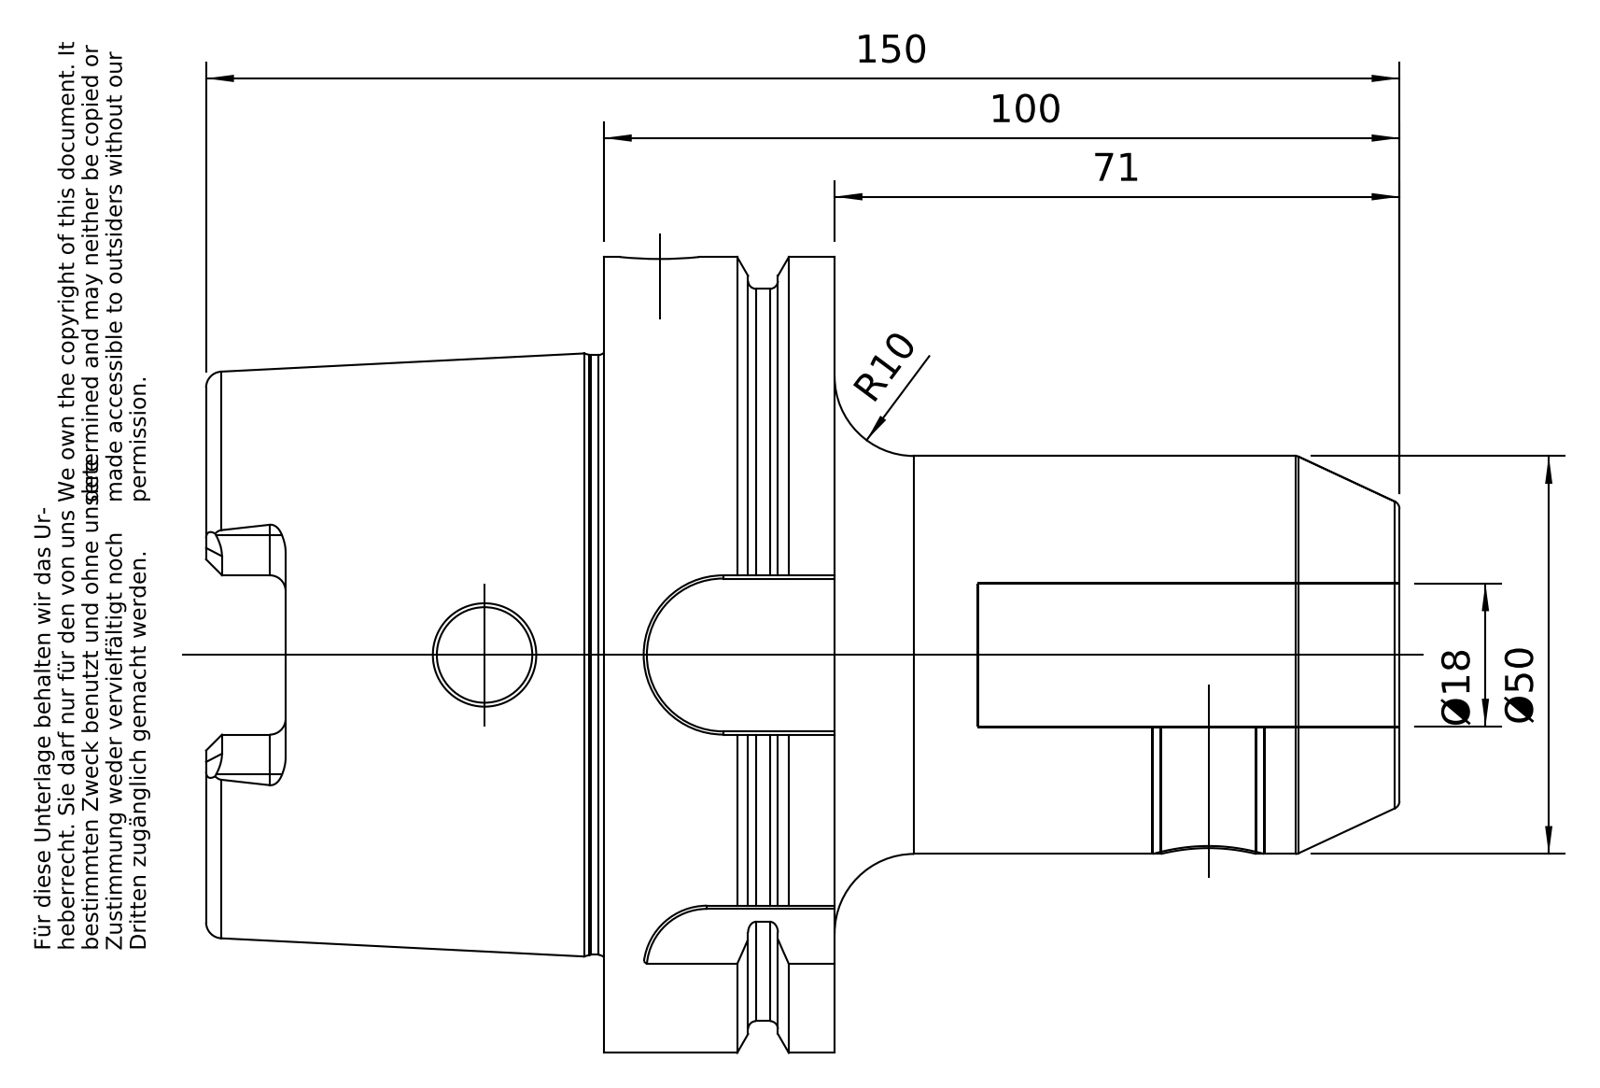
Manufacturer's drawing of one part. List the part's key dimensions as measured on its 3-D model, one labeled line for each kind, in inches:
Part name (STEP PRODUCT): A100-000-18
STEP written by: PRO/ENGINEER BY PARAMETRIC TECHNOLOGY CORPORATION, 2010430 (CONFIG_CONTROL_DESIGN)
Units: inches
Bodies: 1 solid, 180 faces (50 planar, 55 cylindrical, 75 other)
Overall size (bounding box): 5.906 × 3.937 × 3.937
Volume: 22.97 in³ · Surface area: 99.2 in²
Round holes (diameter × count): ⌀0.472 ×2, ⌀0.394 ×1, ⌀0.551 ×1, ⌀0.709 ×1, ⌀0.886 ×1, ⌀0.945 ×1, ⌀0.957 ×1, ⌀0.965 ×1, ⌀2.087 ×1, ⌀2.48 ×1
Round bosses / shafts (diameter × count): ⌀3.937 ×1, ⌀3.622 ×1, ⌀2.967 ×1, ⌀1.969 ×1
Partial cylindrical surfaces — rounded edges, fillets, slot ends (radius × count): R0.079 ×6, R0.197 ×4, R0.315 ×1, R0.394 ×1, R0.433 ×1
Main face-to-face distances: 1.142, 0.492, 0.65, 1.969, 2.461, 3.11, 5.906, 3.937, 3.445, 2.795
Hole centre spacings: 2.717
